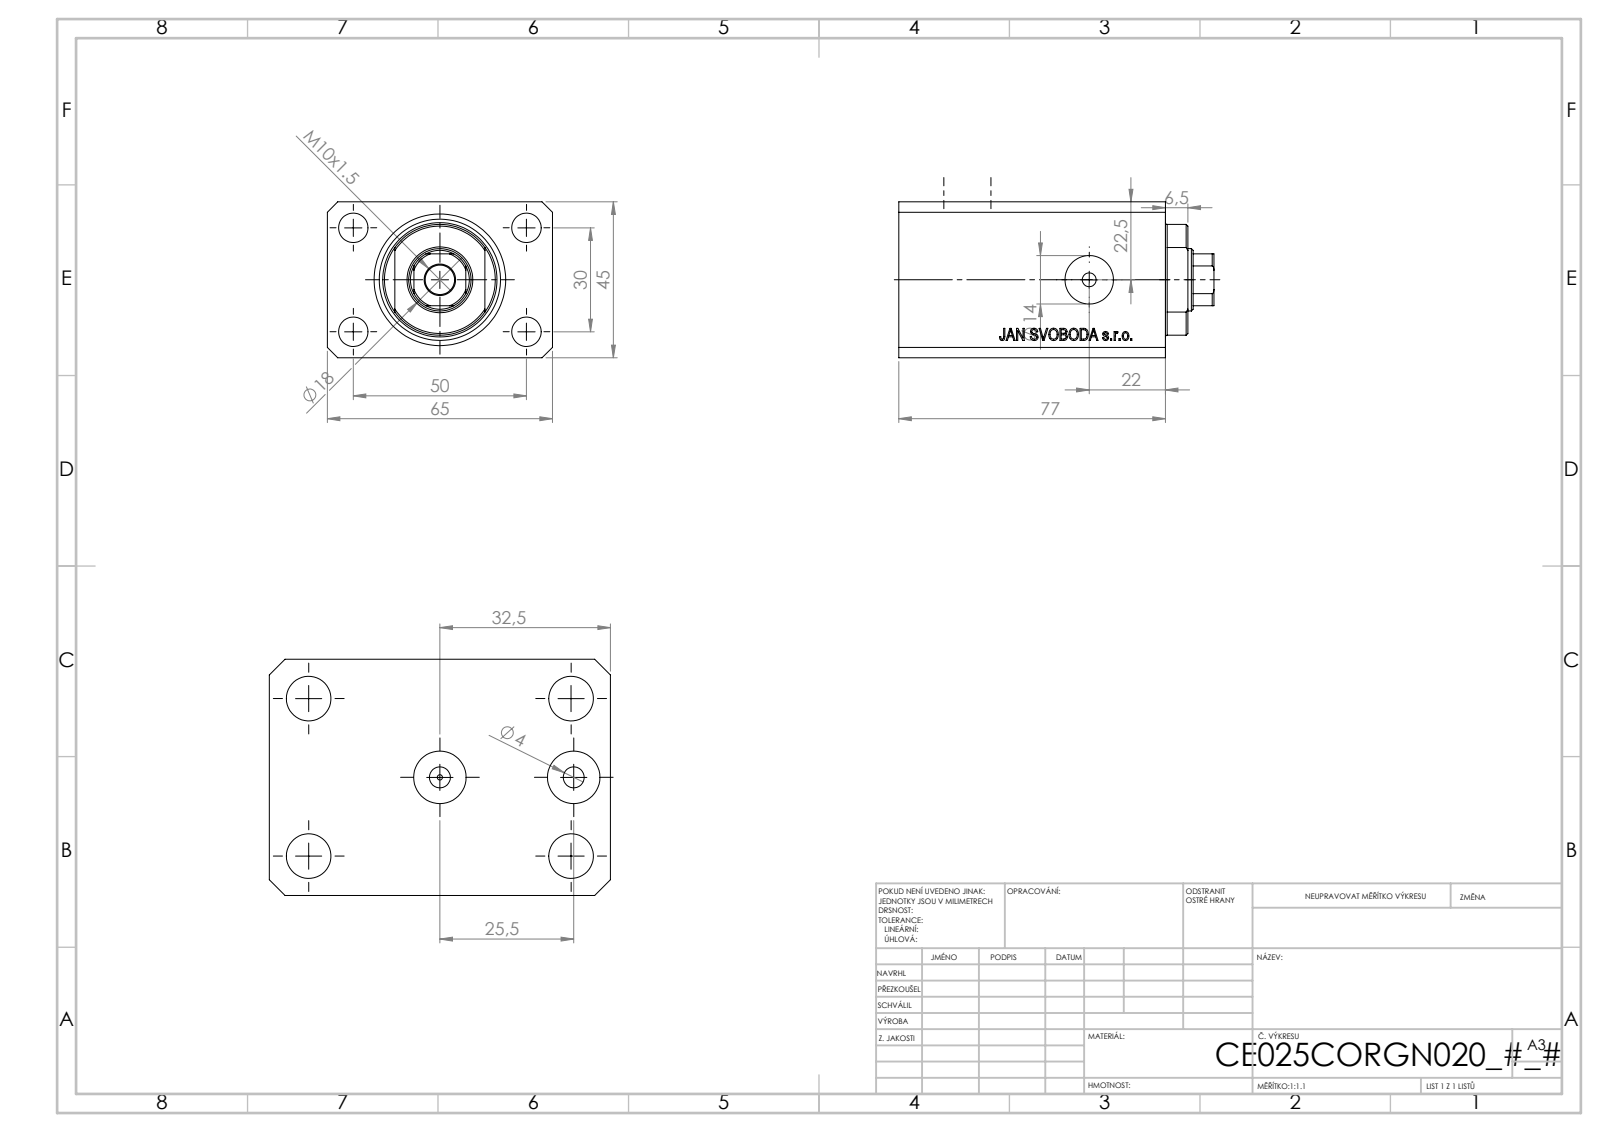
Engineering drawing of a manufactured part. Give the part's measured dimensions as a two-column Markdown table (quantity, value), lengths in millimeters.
| quantity | value |
| --- | --- |
| part name | V250CE_C_Body; V250CE_C_VCP; V250CE_VC_C |
| STEP written by | SolidWorks 2019 (CONFIG_CONTROL_DESIGN) |
| units | millimeters |
| bodies | 3 solids, 872 faces (428 planar, 50 cylindrical, 394 other) |
| overall size | 91 × 65 × 45 |
| volume | 203 440 mm³ |
| surface area | 50 754 mm² |
| round holes (diameter × count) | 8.5 × 5, 4 × 4, 10 × 2, 14 × 2, 1.25 × 1, 18 × 1, 25 × 1, 38 × 1 |
| partial cylindrical surfaces (radius × count) | 8.5 × 1, 16 × 1 |
| main face-to-face distances | 45, 65, 14, 77, 63, 6.9, 56.1, 70.1, 73.52, 20.5 |
| hole center spacings | 29.15, 15.01, 30, 50, 52.68, 58.31, 25.5, 33 |
